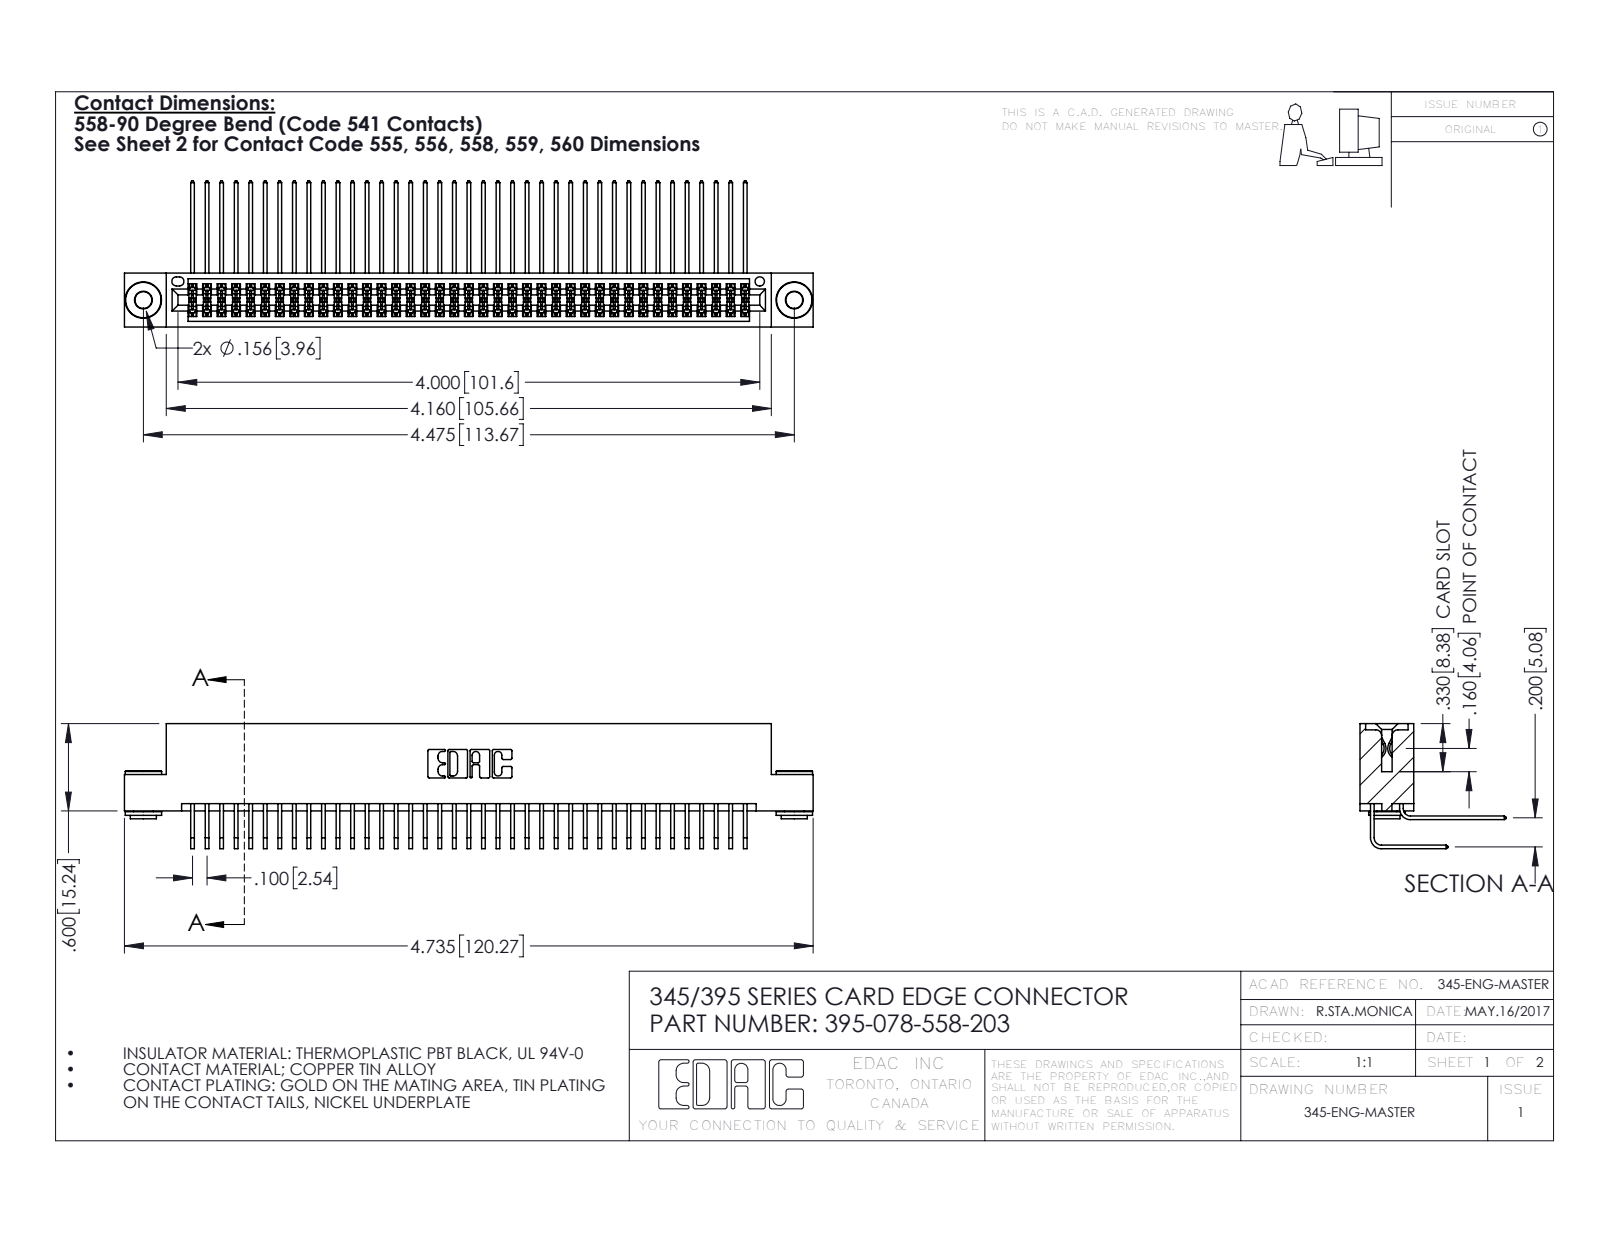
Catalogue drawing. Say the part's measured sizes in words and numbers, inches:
The part is named "345-292-001_558 559 Tail - 1; 345 Part_Flush Mounting Lugs - 0.156 Dia-TH; 395-078-558-203; 345-292-001_558 Tail - 2 (+1 more)". Its 3-D file was written by "SolidWorks 2016 (CONFIG_CONTROL_DESIGN)". It is 81 solids with 4220 faces: 2820 planar, 1392 cylindrical and 8 other. Overall it measures 4.735 by 1.005 by 0.859 inches. Its volume is 0.74 cubic inches and its surface area 31.29 square inches. Round holes: 2 of diameter 0.116, 2 of diameter 0.156, 1 of diameter 0.064. Round bosses or shafts: 2 of diameter 0.25, 2 of diameter 0.18, 2 of diameter 0.136. Partial cylindrical surfaces (rounded edges, fillets, slot ends): 118 of radius 0.006, 22 of radius 0.01, 6 of radius 0.007, 6 of radius 0.031, 3 of radius 0.026, 2 of radius 0.014, 2 of radius 0.019, 2 of radius 0.022. The main face-to-face distances are 0.072, 0.298, 0.2, 0.37, 0.025, 0.098, 0.272, 0.225, 0.025, 0.285. The hole center spacings are 0.27, 4.239, 4.475.
